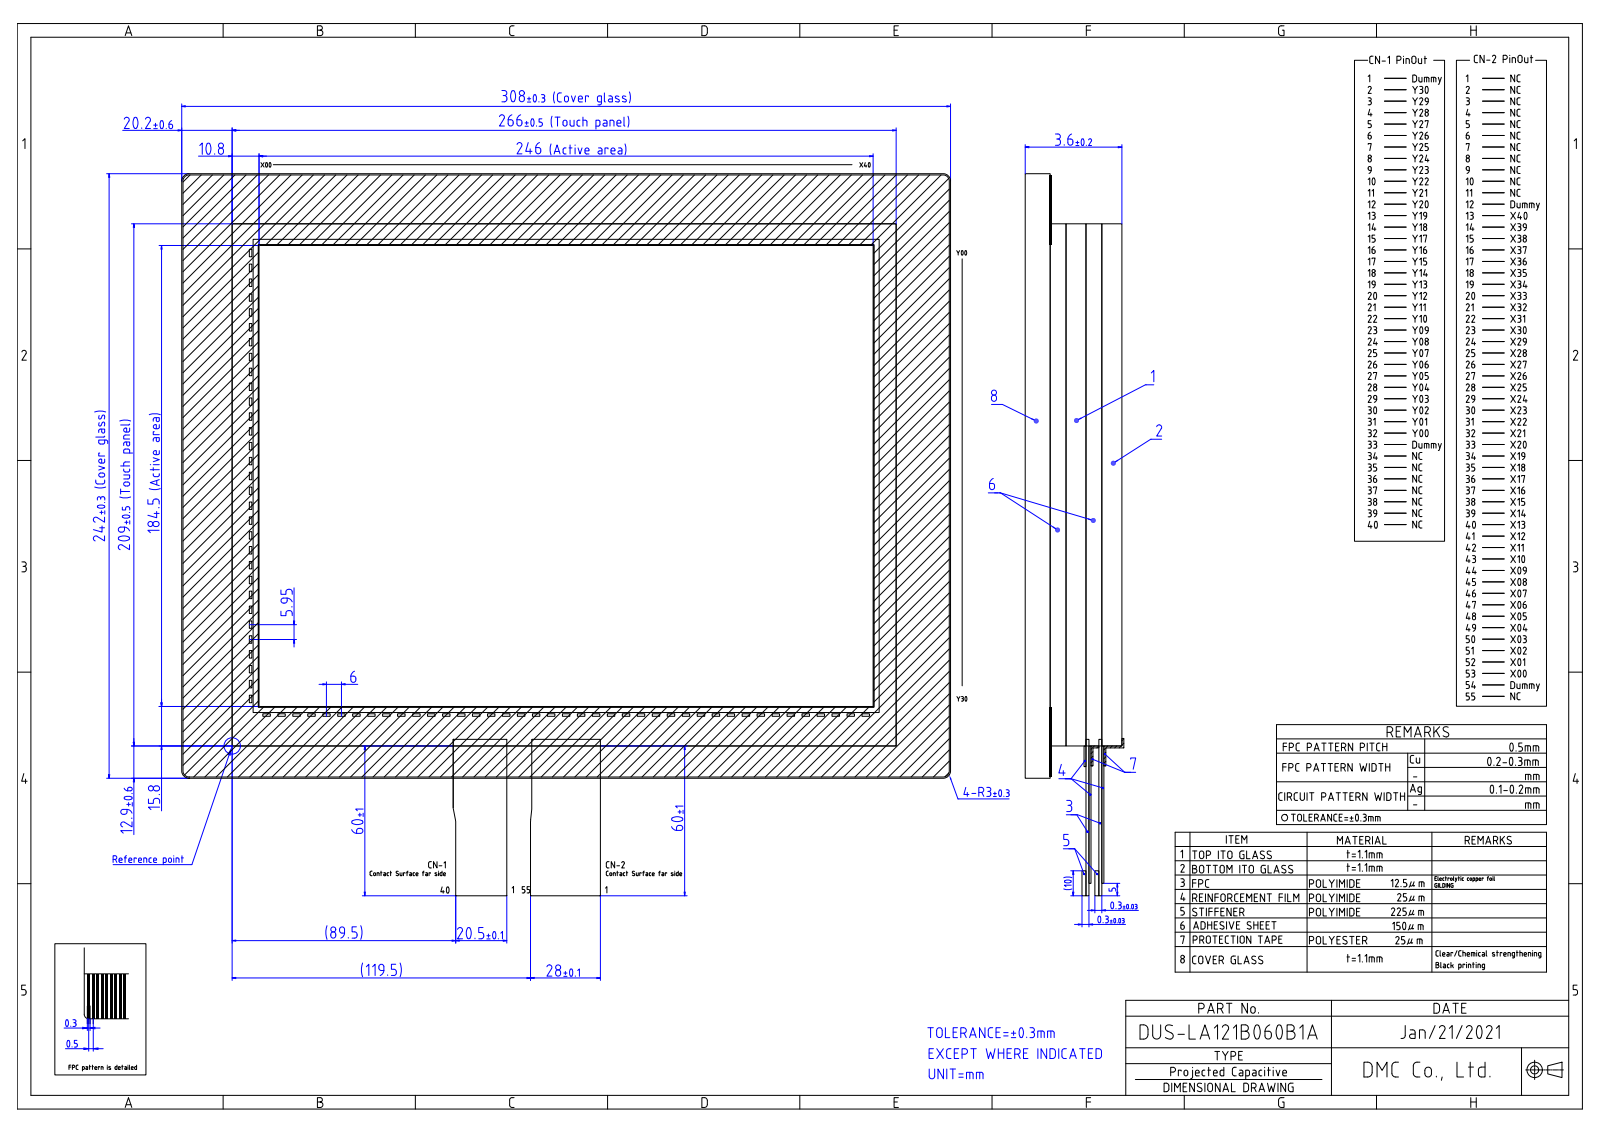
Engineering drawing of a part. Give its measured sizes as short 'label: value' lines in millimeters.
name: DUS-LA121B060B1A
written by: Autodesk Inventor 2020 (CONFIG_CONTROL_DESIGN)
unit: mm
bodies: 1 solid, 425 faces (420 planar, 5 cylindrical, 0 other)
size: 431.2 × 338.8 × 3.6
volume: 216 840 mm³; area: 249 416 mm²
rounds: 4× R3, 1× R0.2
face distances: 1.1, 2.5, 3.6, 1.2, 2.4, 1.25, 1.15, 1.35, 2.45, 2.35
